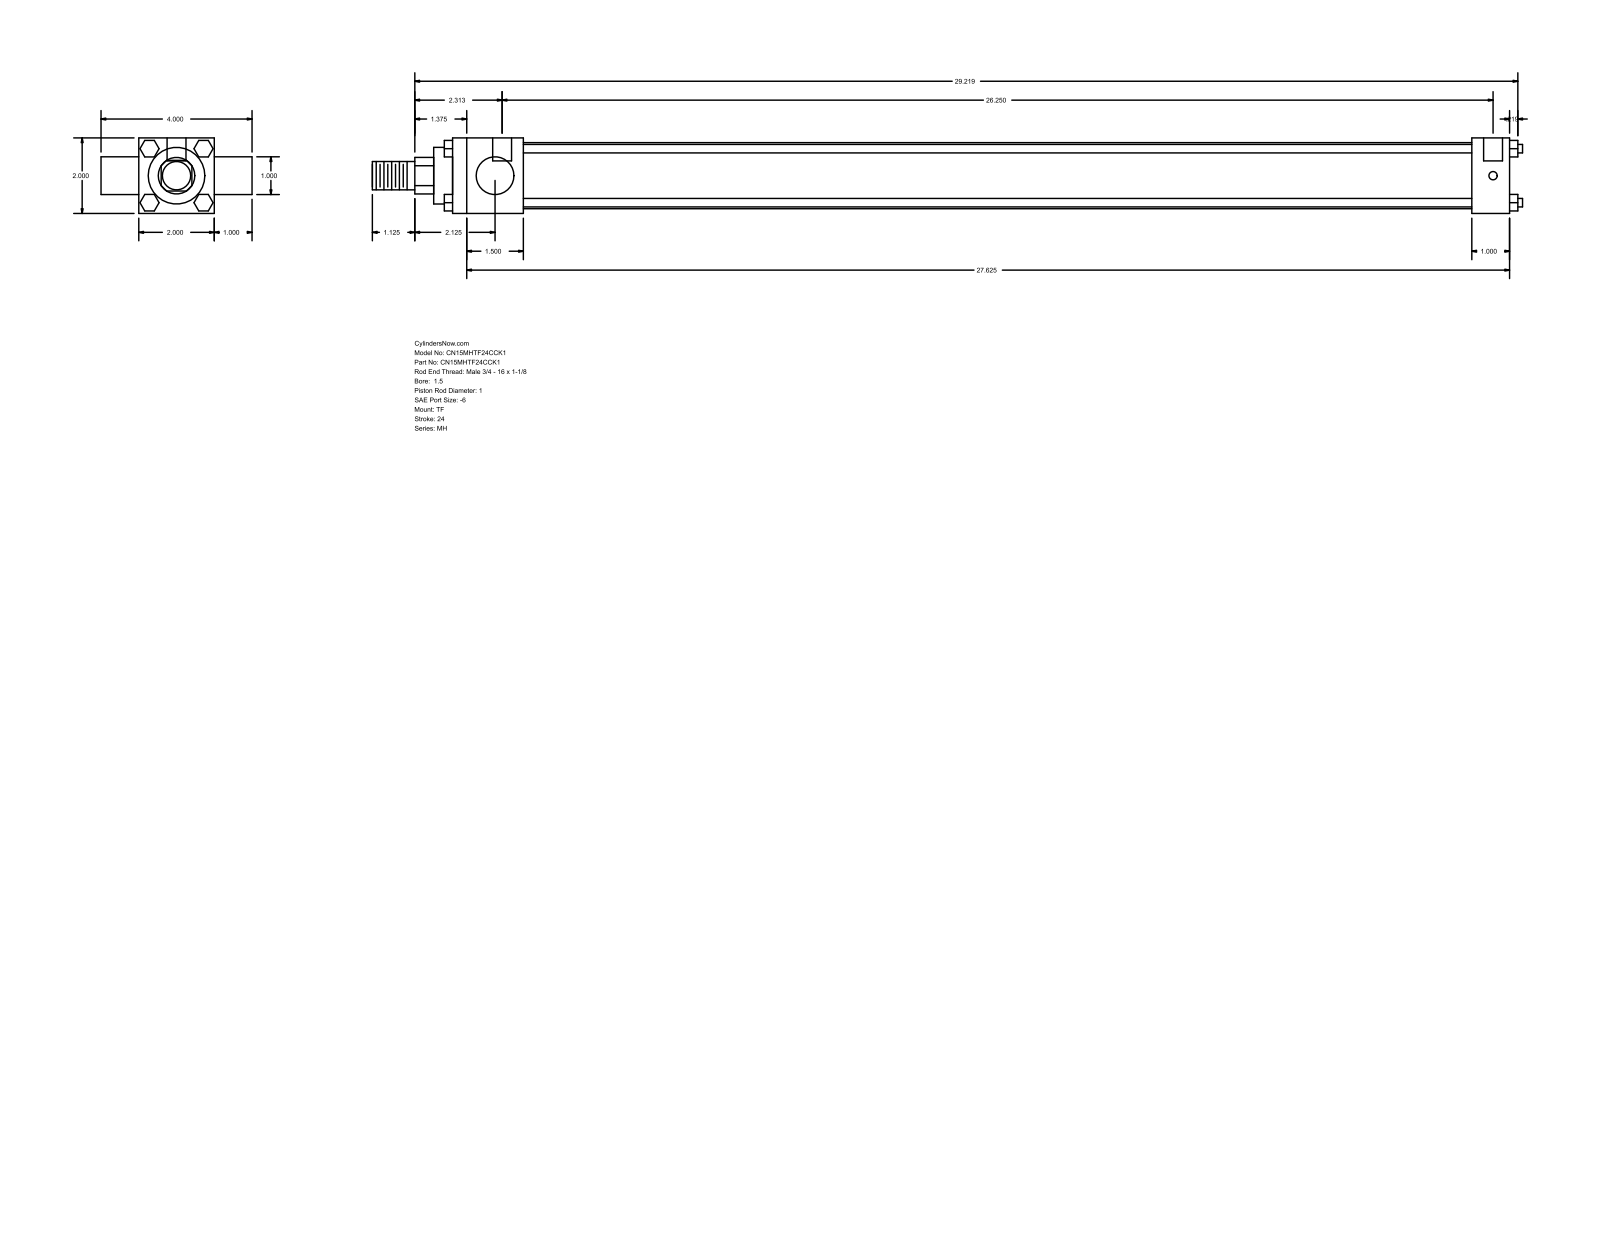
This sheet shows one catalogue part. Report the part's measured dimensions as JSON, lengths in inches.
{"part_name": "MH_TF__0150_1", "step_written_by": "GSSL Pune (CONFIG_CONTROL_DESIGN)", "units": "inches", "bodies": {"solids": 0, "faces": 120, "planar": 92, "cylindrical": 28, "other": 0}, "overall_size": [30.469, 4, 2], "round_holes": [[0.219, 3], [0.5, 2]], "round_bosses_or_shafts": [[0.225, 4], [1, 2], [1.75, 1], [1.5, 1], [0.75, 1]], "partial_cylinders_radius": [[0.484, 1]], "face_to_face_distances": [2, 1, 28, 3, 1.875, 26.125, 27, 25.125, 4, 0.5], "hole_center_spacings": [0.125, 26.25, 26.375]}
